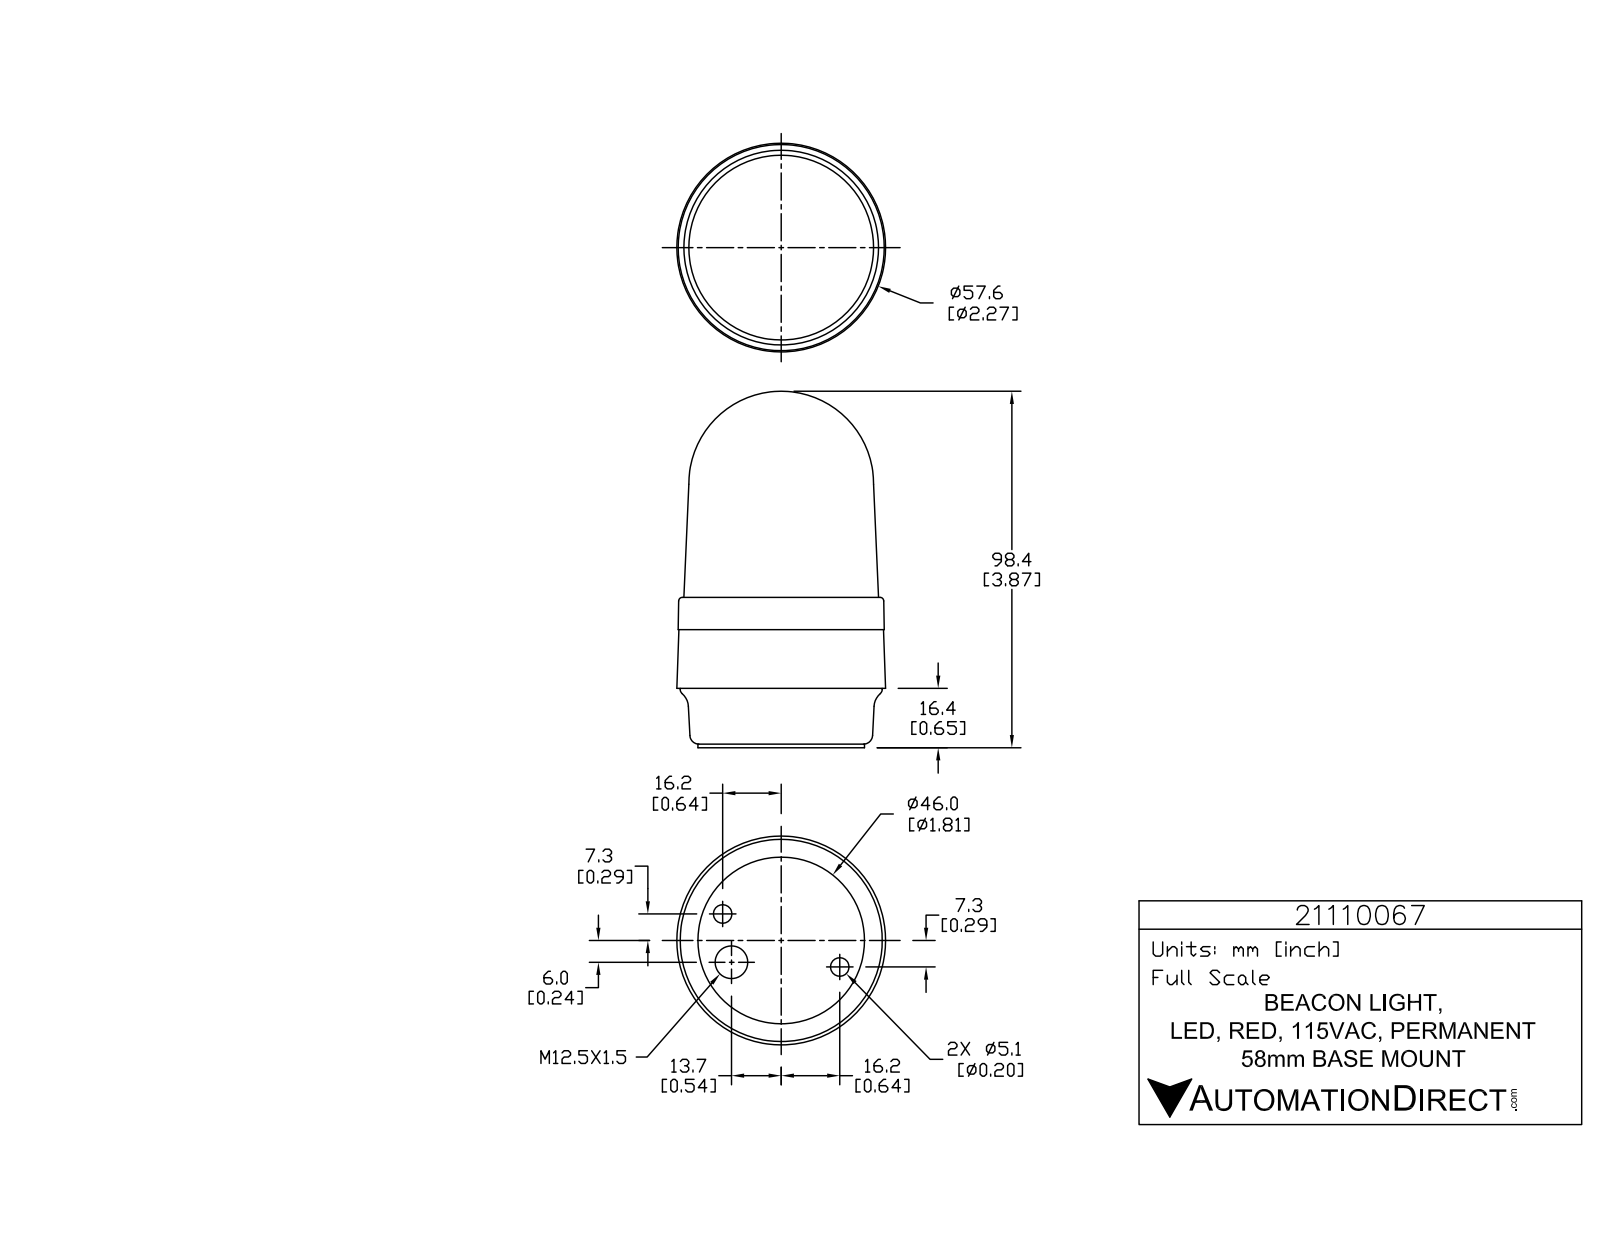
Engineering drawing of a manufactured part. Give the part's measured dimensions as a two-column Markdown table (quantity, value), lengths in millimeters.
| quantity | value |
| --- | --- |
| part name | 21110067 |
| STEP written by | SolidWorks 2015 (AUTOMOTIVE_DESIGN) |
| units | millimeters |
| bodies | 1 solid, 764 faces (527 planar, 145 cylindrical, 92 other) |
| overall size | 98.4 × 57.63 × 57.63 |
| volume | 199 898 mm³ |
| surface area | 18 922 mm² |
| round holes (diameter × count) | 0.99 × 3, 5.11 × 2, 9 × 1 |
| round bosses / shafts (diameter × count) | 5.74 × 3, 1.43 × 3, 55.8 × 1, 46 × 1 |
| partial cylindrical surfaces (radius × count) | 0.2 × 6, 0.21 × 6, 0.21 × 6, 3.32 × 6, 0.1 × 3, 0.12 × 3, 0.19 × 3, 0.2 × 3 |
| main face-to-face distances | 16.4, 1, 15.4, 41.5, 40.5, 25.1, 32.6, 31.6, 16.2, 8.9 |
| hole center spacings | 13.56, 29.94, 35.5 |
